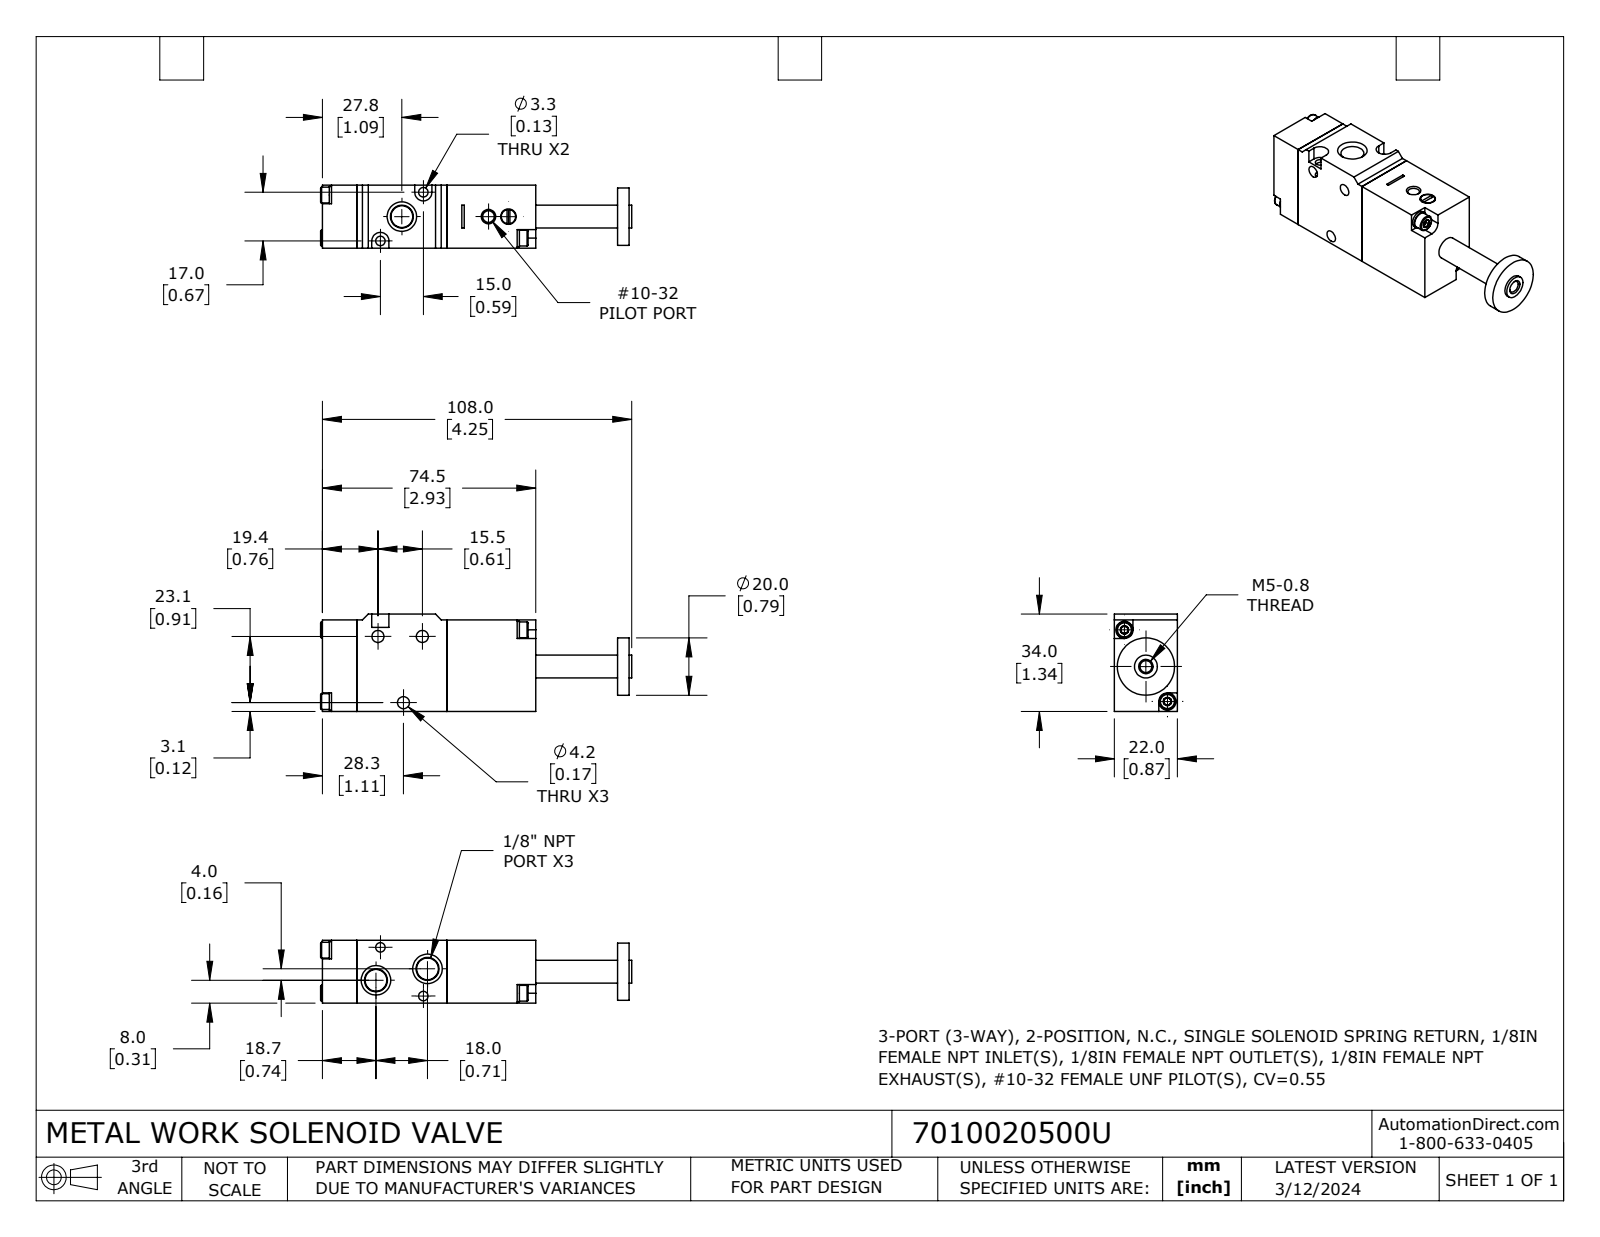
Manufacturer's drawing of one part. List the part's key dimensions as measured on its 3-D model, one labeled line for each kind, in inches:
Part name (STEP PRODUCT): 7010020500U
STEP written by: SolidWorks 2023 (CONFIG_CONTROL_DESIGN)
Units: inches
Bodies: 11 solids, 265 faces (125 planar, 66 cylindrical, 74 other)
Overall size (bounding box): 4.276 × 1.339 × 0.866
Volume: 3.244 in³ · Surface area: 26.61 in²
Round holes (diameter × count): ⌀0.118 ×4, ⌀0.165 ×3, ⌀0.13 ×2, ⌀0.159 ×1, ⌀0.163 ×1, ⌀0.213 ×1
Round bosses / shafts (diameter × count): ⌀0.236 ×4, ⌀0.217 ×4, ⌀0.787 ×1, ⌀0.315 ×1, ⌀0.197 ×1
Partial cylindrical surfaces — rounded edges, fillets, slot ends (radius × count): R0.118 ×2
Main face-to-face distances: 0.866, 1.24, 1.26, 0.472, 1.713, 1.22, 2.933, 2.461, 1.339, 0.079
Hole centre spacings: 0.564, 0.584, 0.591, 0.984, 1.148, 0.274, 0.61, 0.893
